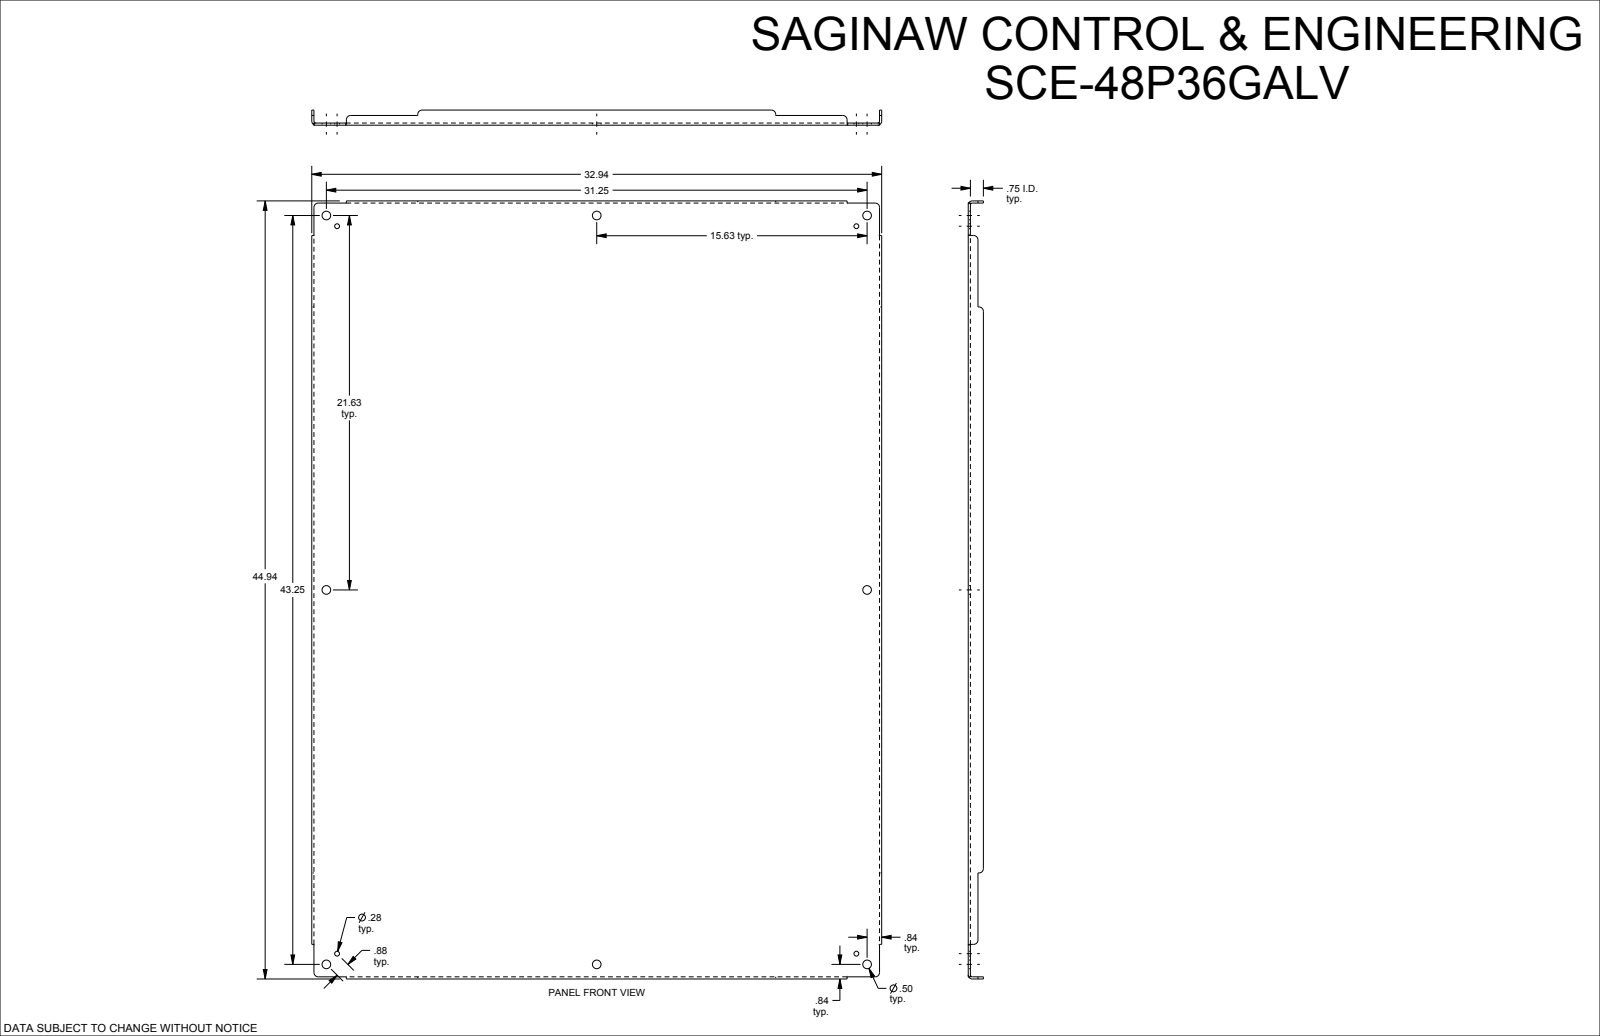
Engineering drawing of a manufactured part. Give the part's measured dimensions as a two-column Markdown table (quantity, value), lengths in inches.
| quantity | value |
| --- | --- |
| part name | SCE-48P36GALV |
| STEP written by | SolidWorks 2019 (CONFIG_CONTROL_DESIGN) |
| units | inches |
| bodies | 1 solid, 110 faces (46 planar, 40 cylindrical, 24 other) |
| overall size | 44.938 × 32.938 × 0.875 |
| volume | 195 in³ |
| surface area | 3 142 in² |
| round holes (diameter × count) | 0.5 × 8, 0.281 × 4 |
| partial cylindrical surfaces (radius × count) | 0.25 × 12, 0.112 × 4, 0.237 × 4 |
| main face-to-face distances | 0.125, 0.125, 32.813, 44.813, 32.687, 32.938, 44.687, 44.938, 0.75, 0.875 |
| hole center spacings | 0.875, 15.019, 15.625, 21.015, 21.625, 26.679, 30.638, 37.143 |
